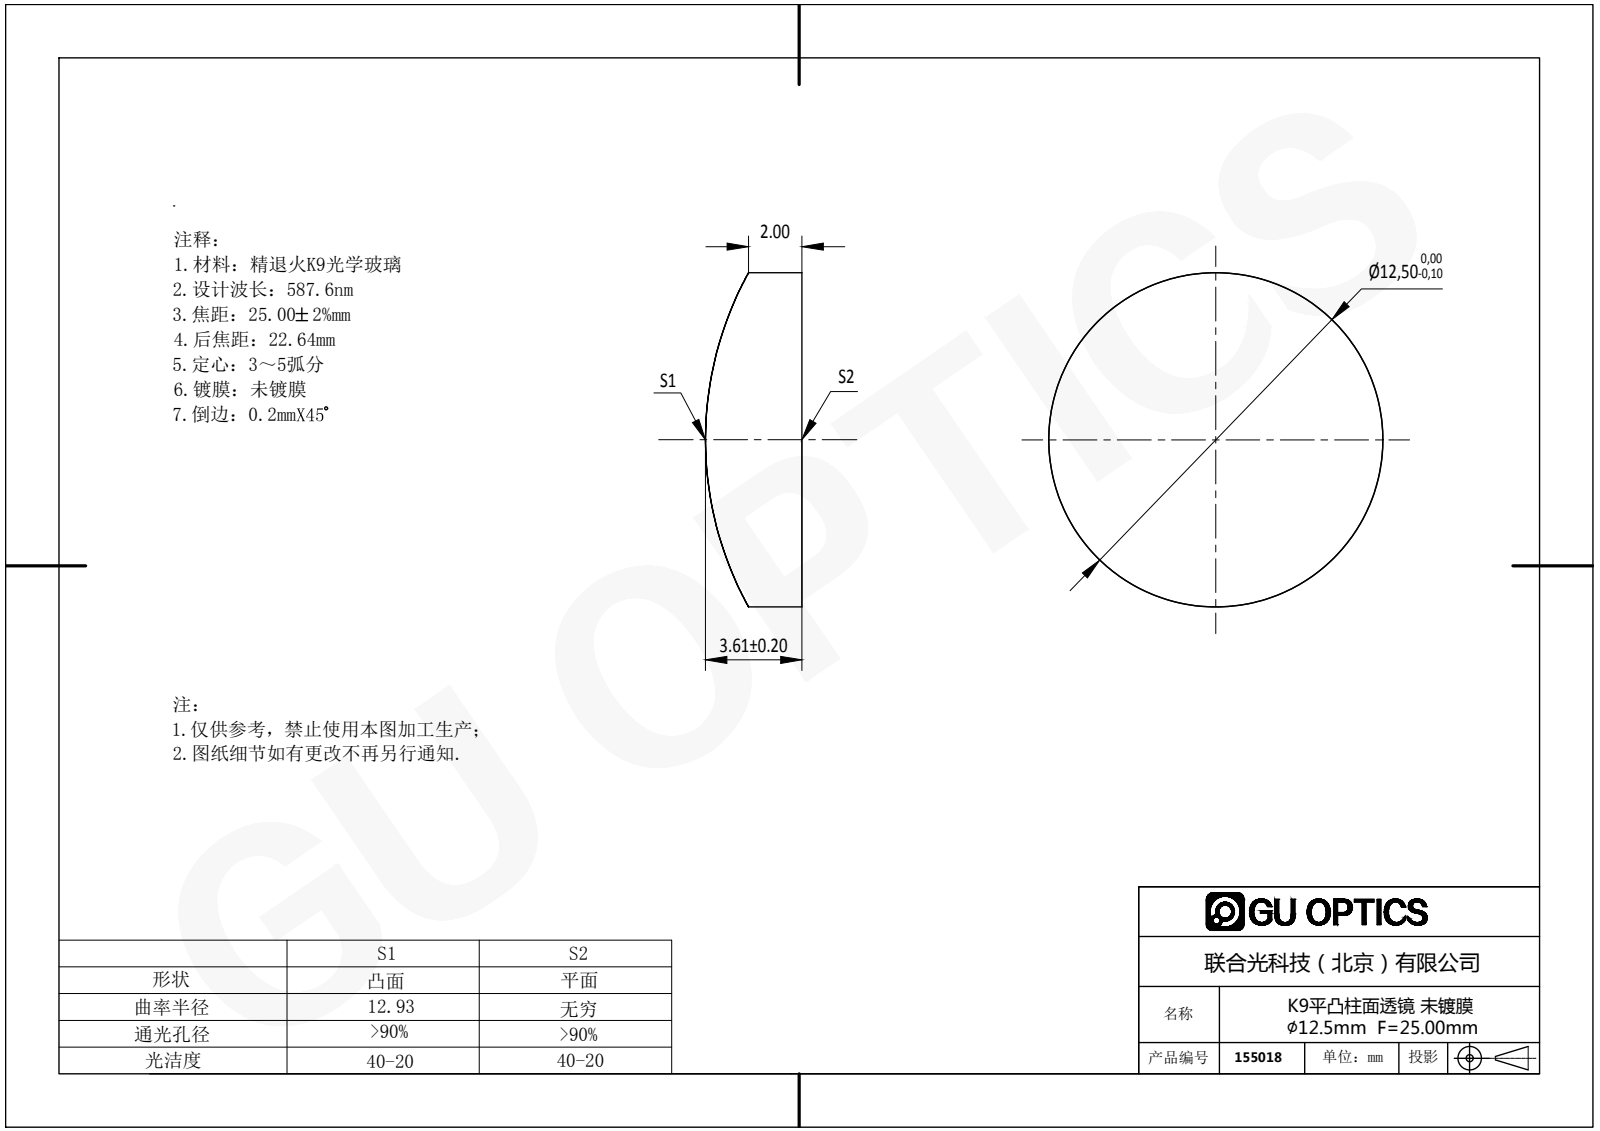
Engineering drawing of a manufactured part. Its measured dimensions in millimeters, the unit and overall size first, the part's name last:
Units: millimetres
Overall size (bounding box): 12.5 × 12.5 × 3.61
Round bosses / shafts (diameter × count): ⌀12.5 ×1
Partial cylindrical surfaces — rounded edges, fillets, slot ends (radius × count): R12.93 ×1
Volume: 395 mm³ · Surface area: 360 mm²
Bodies: 1 solid, 4 faces (1 planar, 3 cylindrical, 0 other)
Part name (STEP PRODUCT): 155018
STEP written by: SolidWorks 2016 (AUTOMOTIVE_DESIGN)
